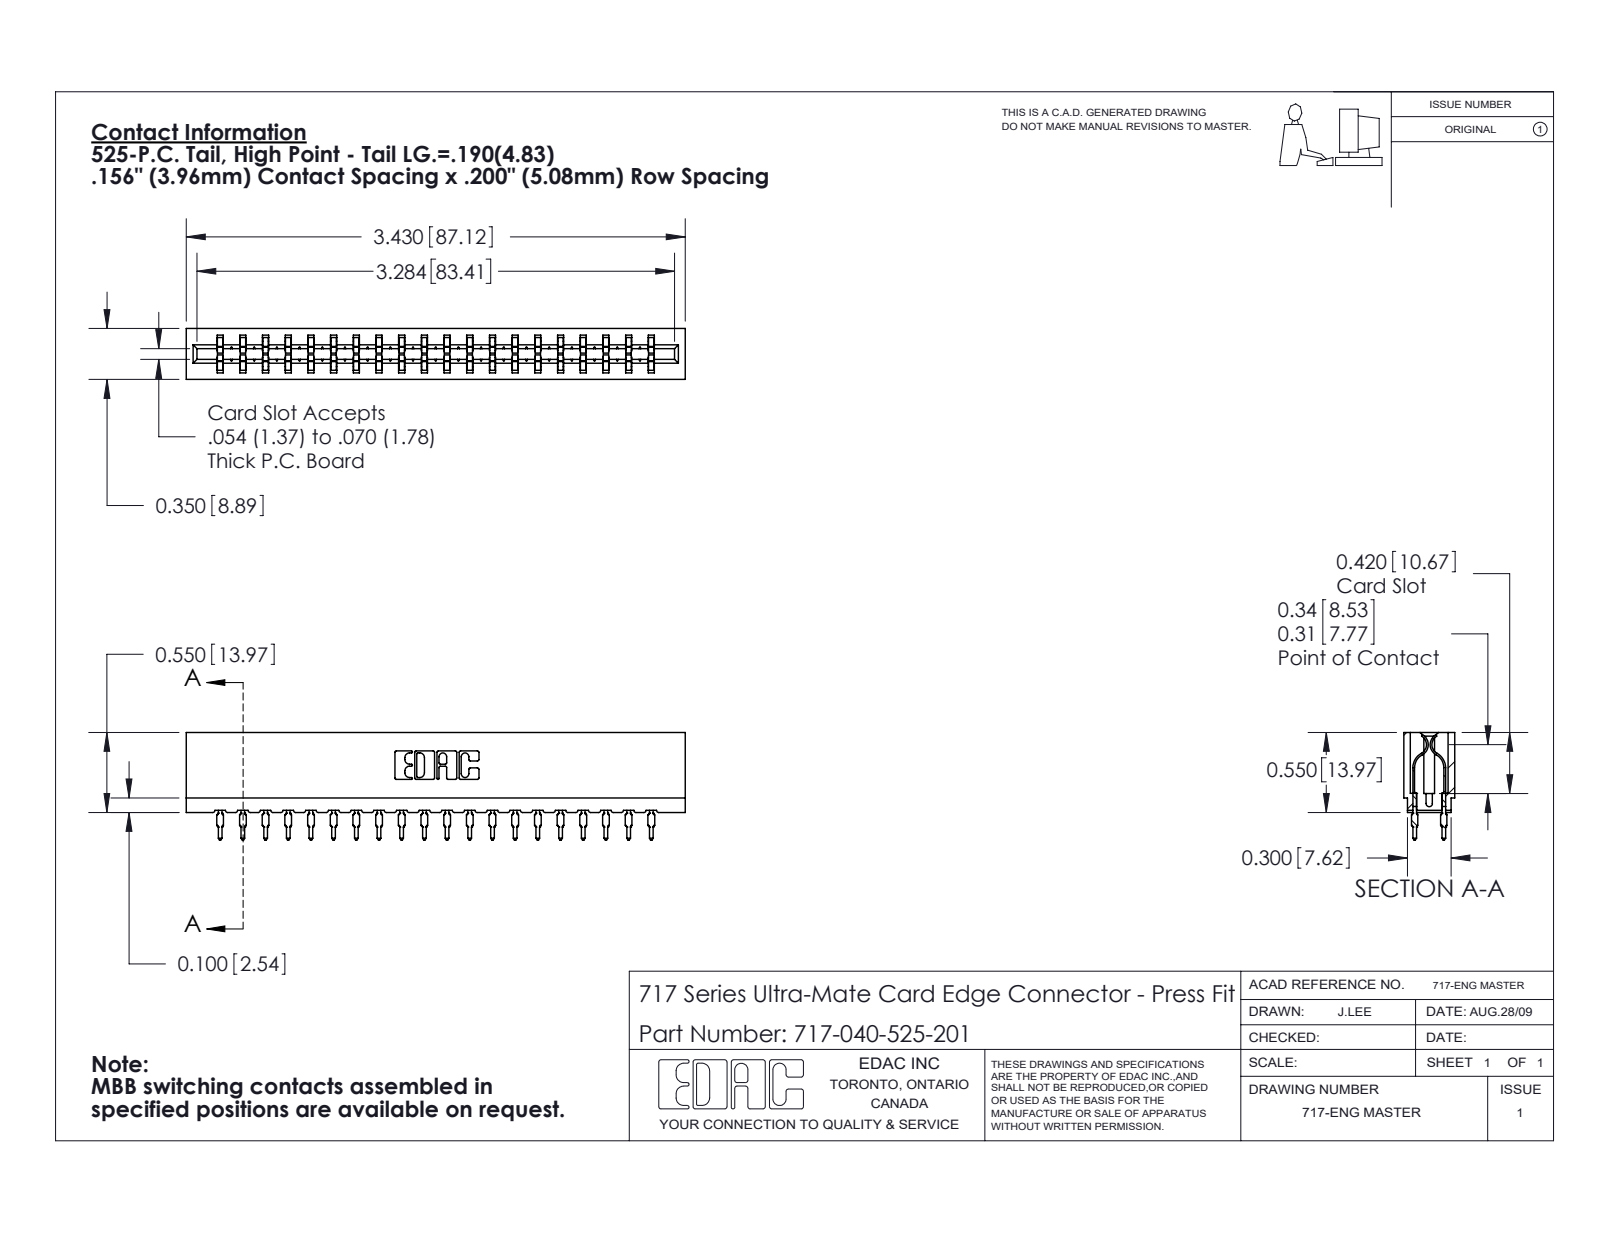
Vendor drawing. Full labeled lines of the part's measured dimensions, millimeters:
Part name (STEP PRODUCT): 745-292-001_525; 717 Part_Insulator Option - 06; 717-040-525-201
STEP written by: SolidWorks 2020 (CONFIG_CONTROL_DESIGN)
Units: millimetres
Bodies: 41 solids, 3694 faces (1914 planar, 740 cylindrical, 1040 other)
Overall size (bounding box): 87.1 × 18.8 × 8.9
Volume: 7 640 mm³ · Surface area: 11 330 mm²
Partial cylindrical surfaces — rounded edges, fillets, slot ends (radius × count): R0.5 ×80, R0.4 ×40, R0.3 ×22, R0.1 ×8, R0.3 ×8, R0.2 ×6, R0.8 ×6, R0.7 ×3
Main face-to-face distances: 5.4, 3.5, 8.9, 4, 1.6, 7.3, 1.9, 3.8, 1.9, 15.8
